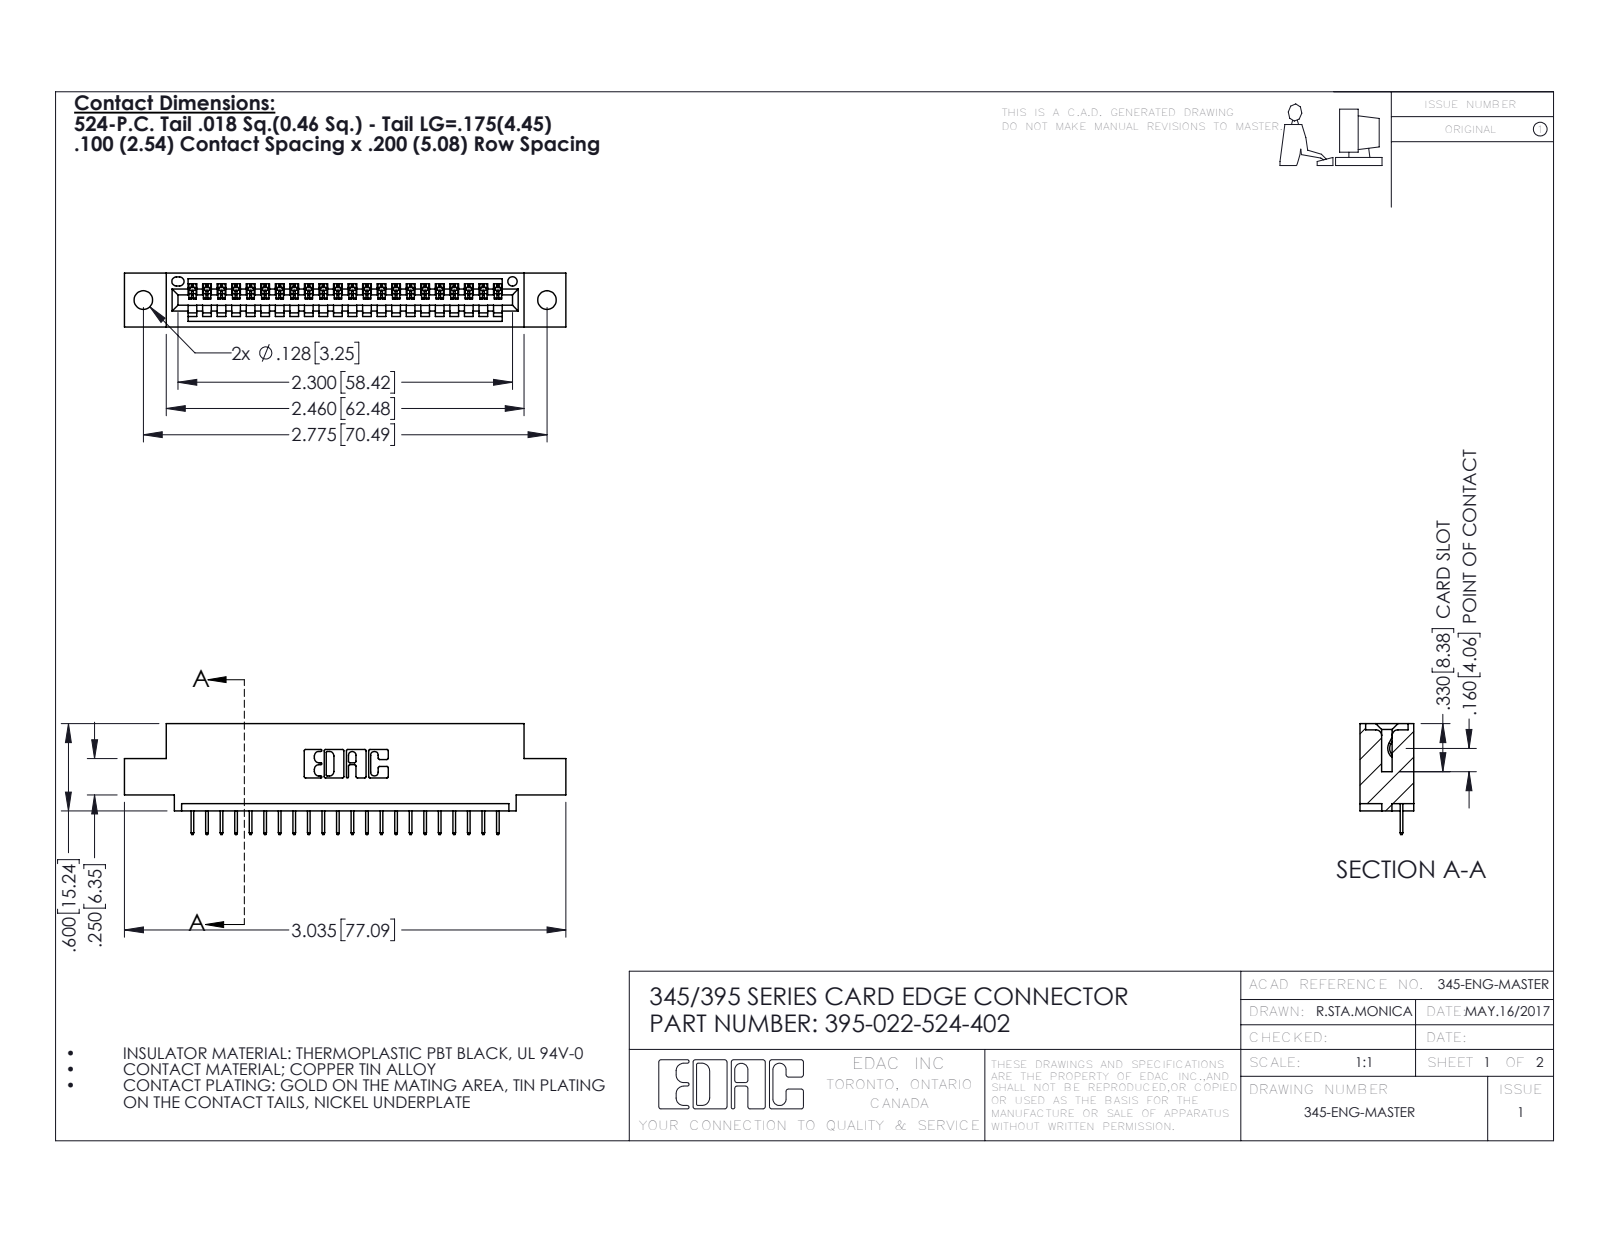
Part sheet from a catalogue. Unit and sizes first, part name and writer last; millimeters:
Units: millimetres
Overall size (bounding box): 77.1 × 19.4 × 9.4
Round holes (diameter × count): ⌀3.3 ×2, ⌀1.6 ×1
Partial cylindrical surfaces — rounded edges, fillets, slot ends (radius × count): R0.2 ×44, R0.3 ×22, R0.2 ×6, R0.8 ×6, R0.7 ×3, R0.8 ×2, R1 ×2, R0.4 ×1
Main face-to-face distances: 1.8, 7.6, 9.4, 5.1, 2.5, 6.9, 0.6, 5.7, 1.8, 3.8
Hole centre spacings: 6.9, 64.5, 70.5
Volume: 6 960 mm³ · Surface area: 8 510 mm²
Bodies: 23 solids, 1494 faces (1096 planar, 398 cylindrical, 0 other)
Part name (STEP PRODUCT): 345-292-001_345-293-124; 395-022-524-402; 345 Part_0.110 Offset - 0.128 Dia
STEP written by: SolidWorks 2016 (CONFIG_CONTROL_DESIGN)
